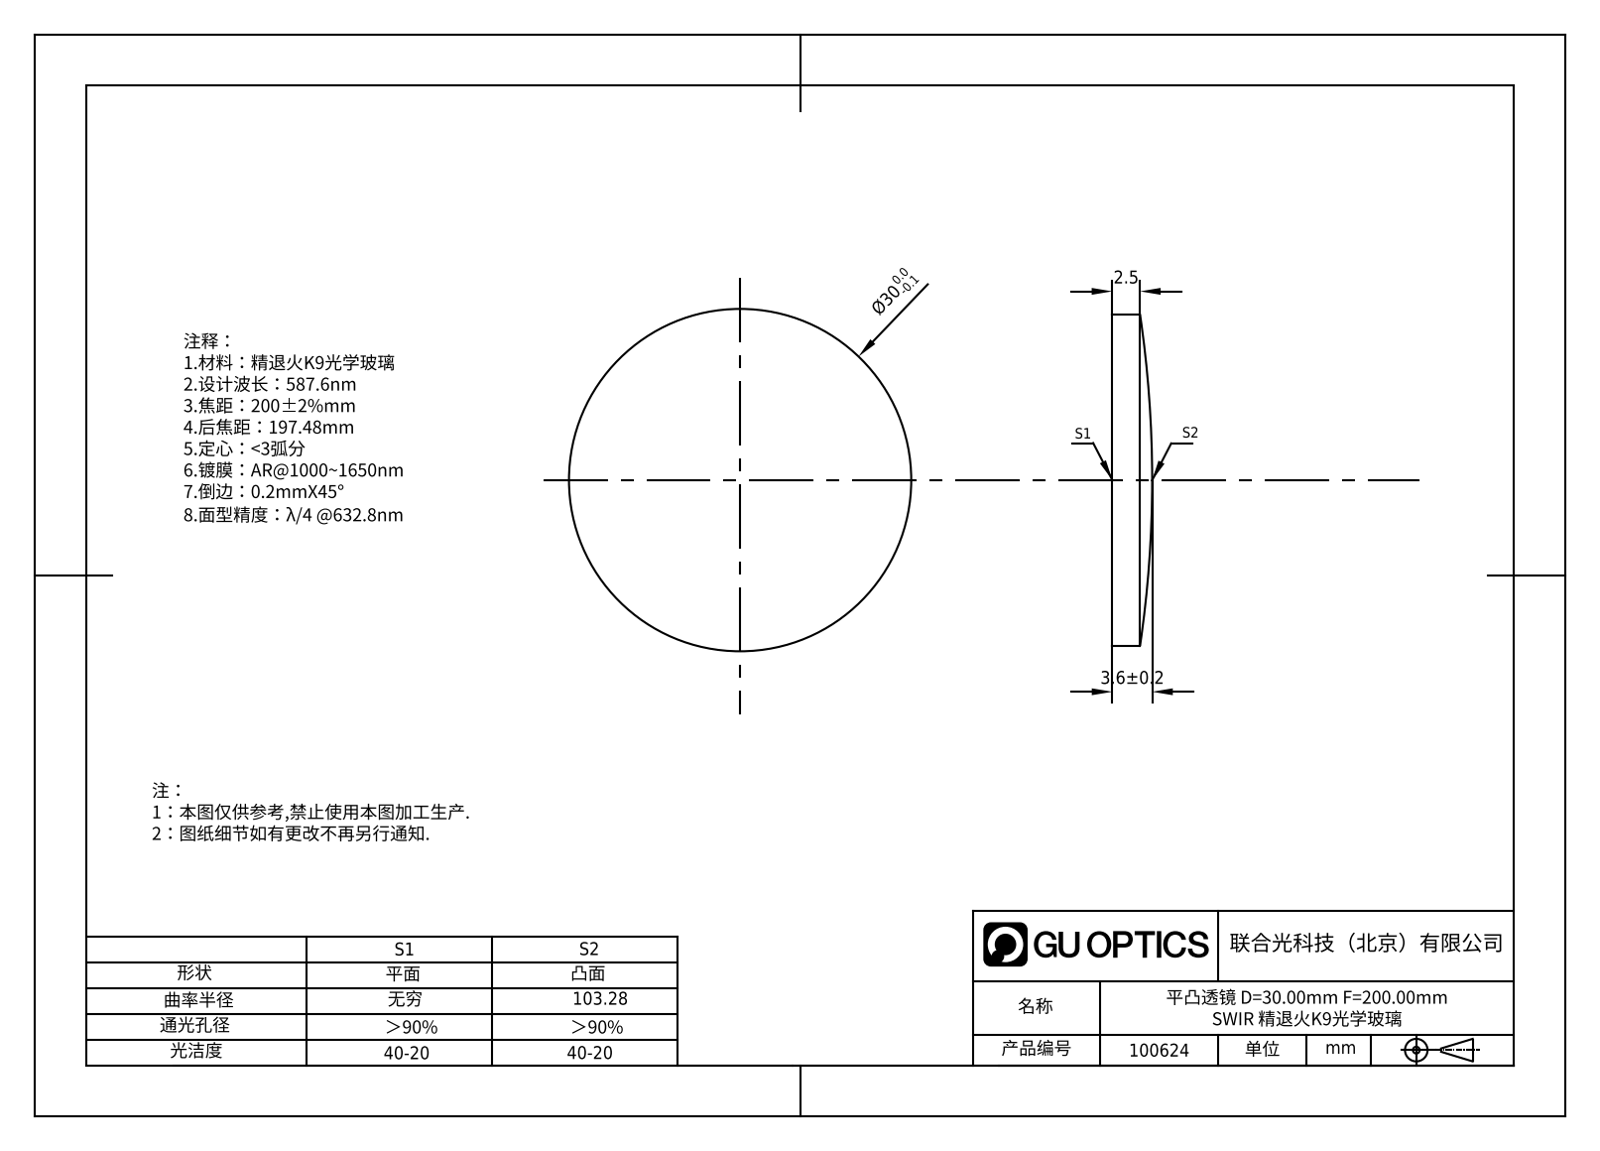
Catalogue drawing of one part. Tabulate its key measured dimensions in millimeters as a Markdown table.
| quantity | value |
| --- | --- |
| part name | 100601 |
| STEP written by | SolidWorks 2020 (CONFIG_CONTROL_DESIGN) |
| units | millimeters |
| bodies | 1 solid, 5 faces (1 planar, 2 cylindrical, 2 other) |
| overall size | 30 × 30 × 3.6 |
| volume | 2 156 mm³ |
| surface area | 1 653 mm² |
| round bosses / shafts (diameter × count) | 30 × 1 |
